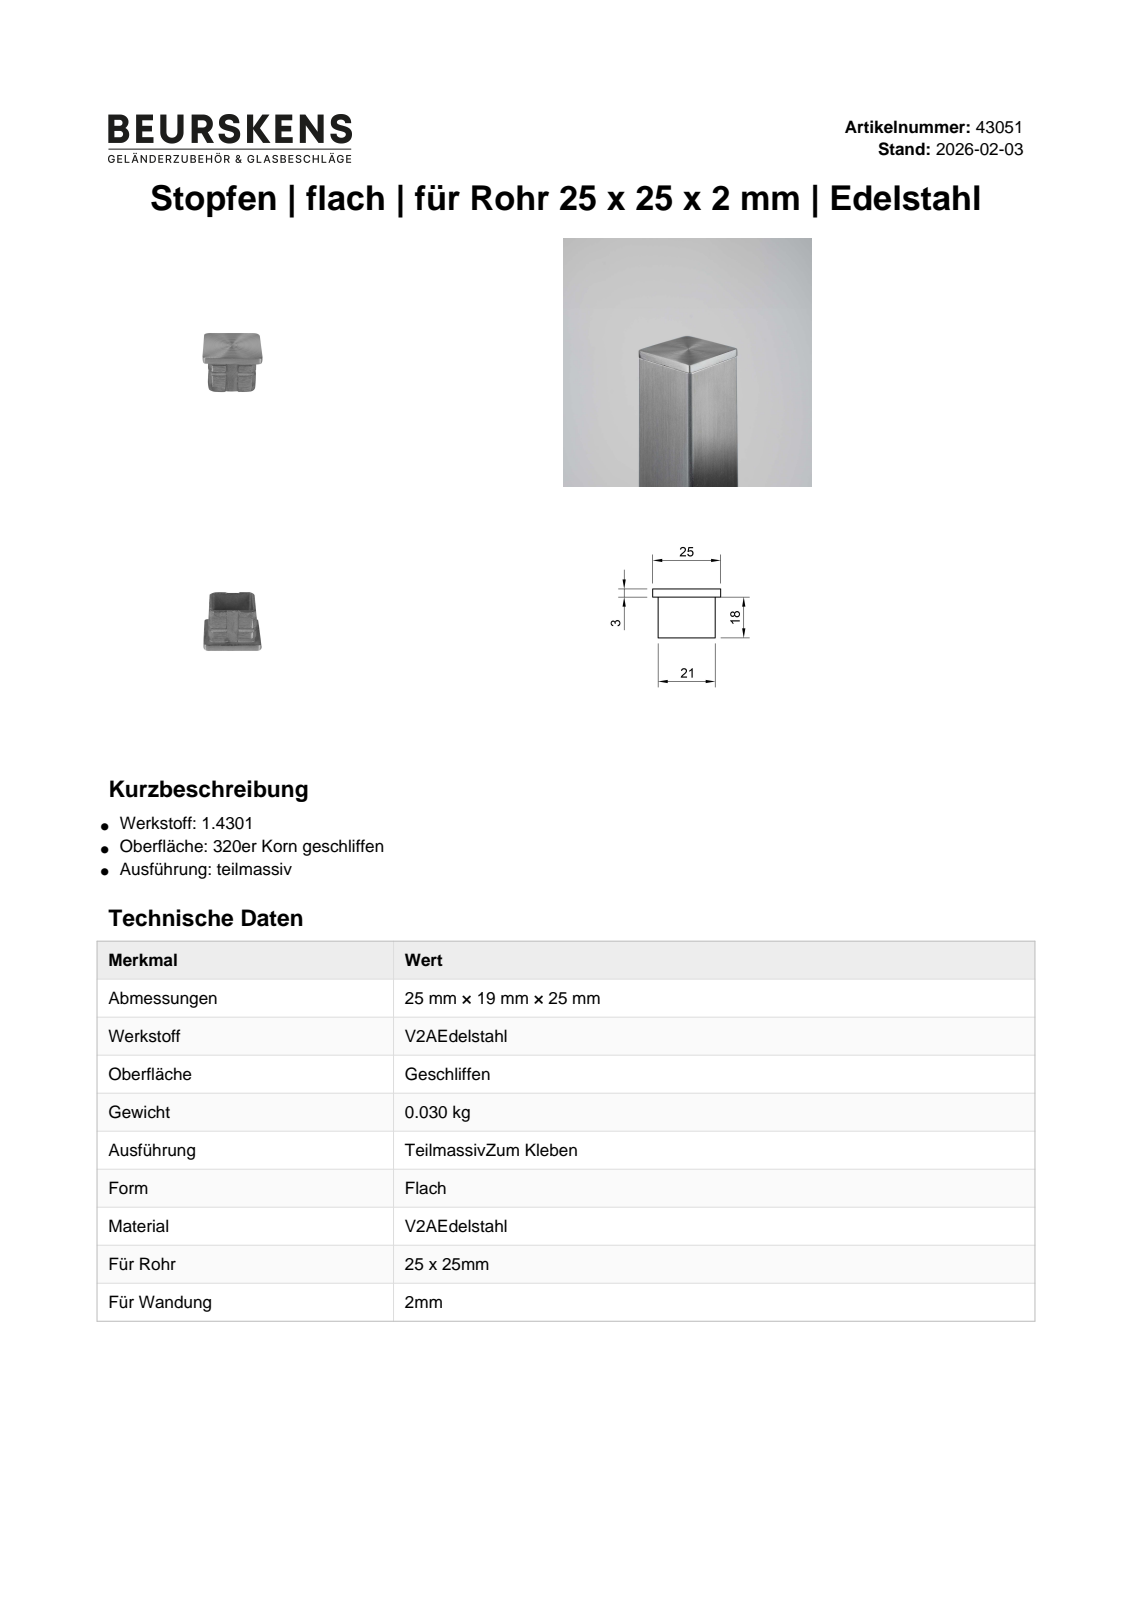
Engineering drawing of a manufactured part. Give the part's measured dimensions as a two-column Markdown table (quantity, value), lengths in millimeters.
| quantity | value |
| --- | --- |
| part name | 43051 |
| STEP written by | Autodesk Inventor 2022 (AUTOMOTIVE_DESIGN) |
| units | millimeters |
| bodies | 1 solid, 24 faces (16 planar, 8 cylindrical, 0 other) |
| overall size | 25 × 25 × 18 |
| volume | 3 804 mm³ |
| surface area | 3 829 mm² |
| partial cylindrical surfaces (radius × count) | 2 × 8 |
| main face-to-face distances | 2, 19, 21, 17, 4, 23, 1, 3, 15, 16 |
